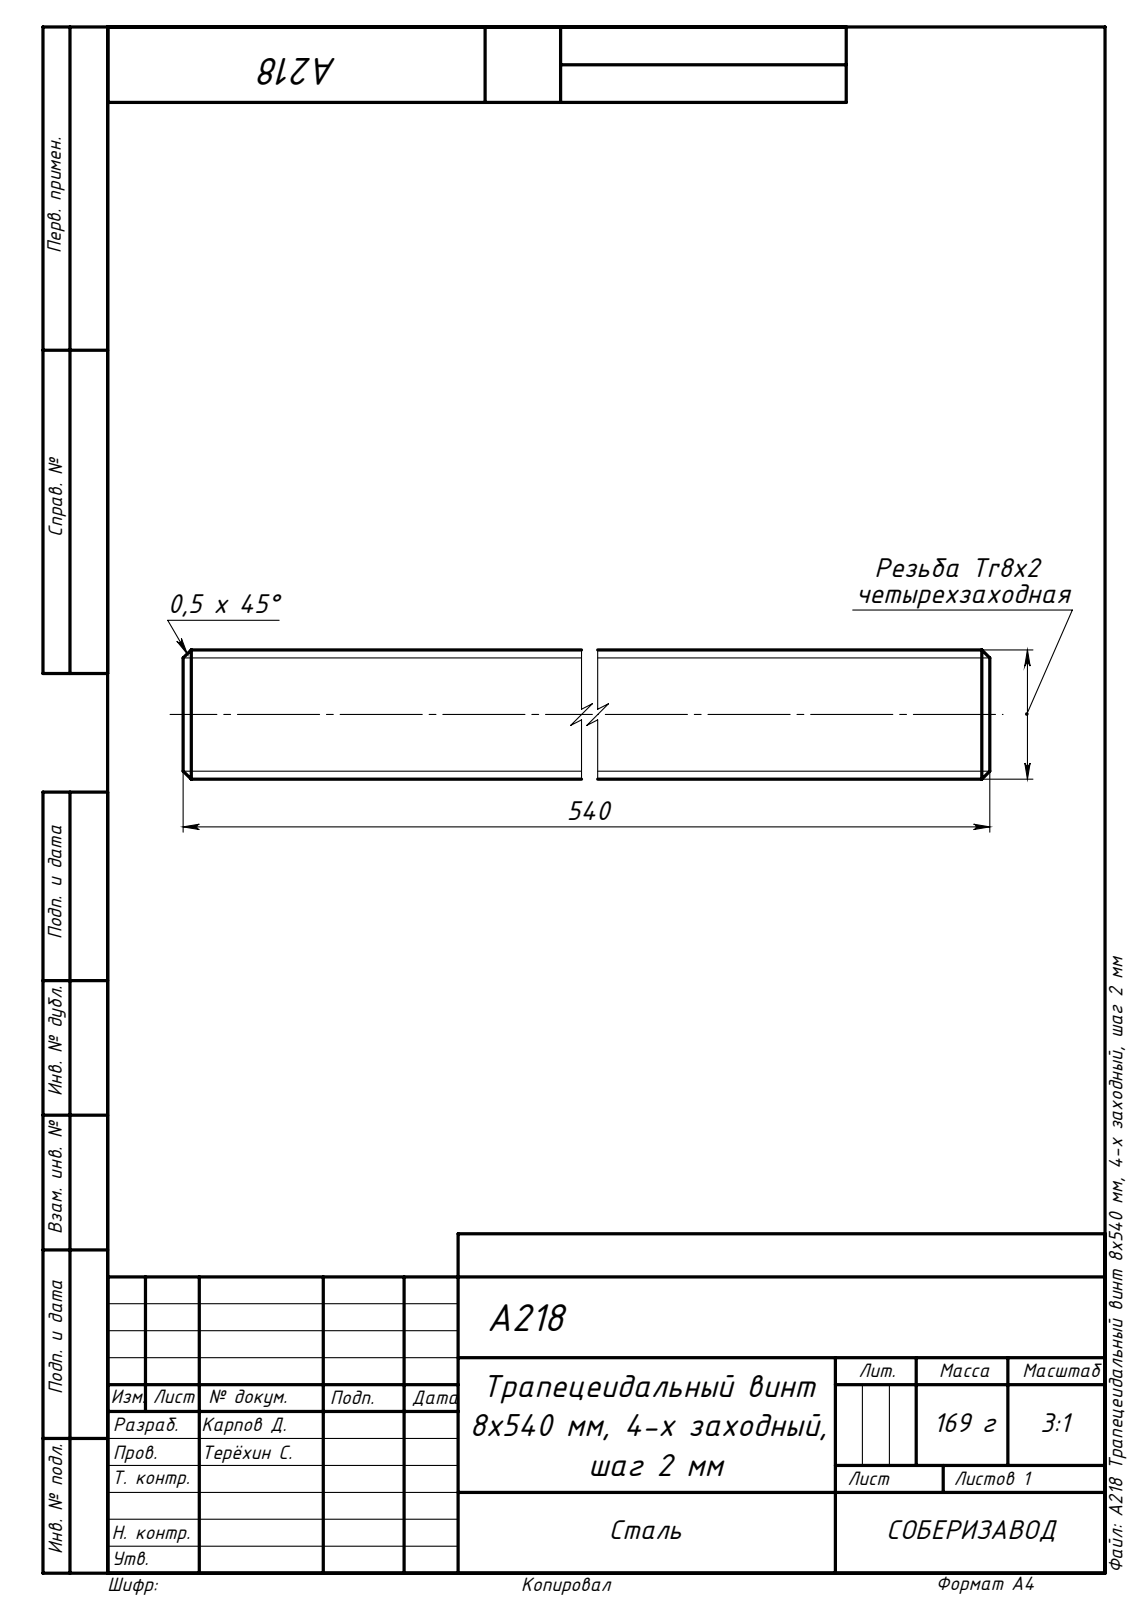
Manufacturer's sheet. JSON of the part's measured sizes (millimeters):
{"part_name": "A218 Трапецеидальный винт 8х540 мм, 4-х заходный, шаг 2 мм", "step_written_by": "SolidWorks 2018 (AUTOMOTIVE_DESIGN)", "units": "millimeters", "bodies": {"solids": 1, "faces": 4, "planar": 2, "cylindrical": 2, "other": 0}, "overall_size": [540, 8, 8], "volume_mm3": 27143, "surface_area_mm2": 13672, "round_bosses_or_shafts": [[8, 1]], "face_to_face_distances": [540]}
